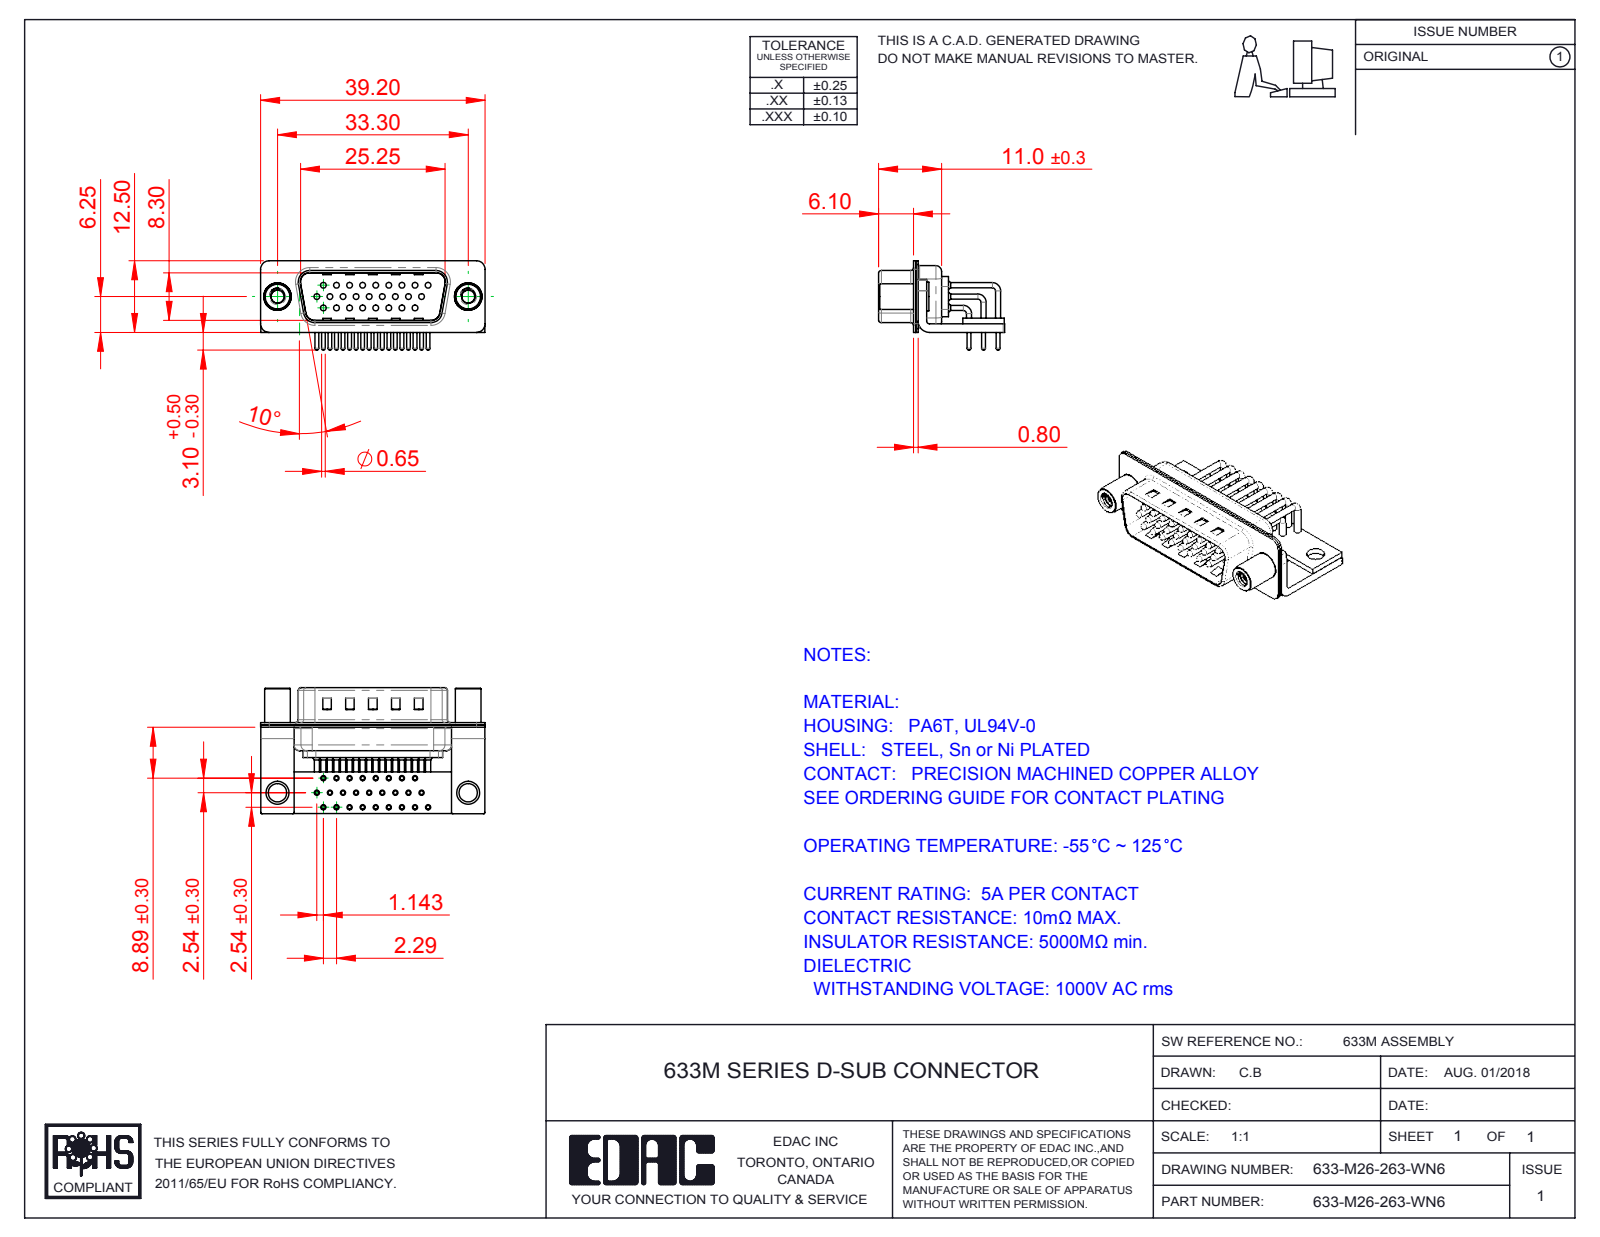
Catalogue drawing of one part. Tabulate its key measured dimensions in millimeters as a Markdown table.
| quantity | value |
| --- | --- |
| part name | 633-M26-263-WN6; 633M Stabilizer Bracket; 633M Housing_26 Contacts; 633M 4-40 Threaded Standoff (+6 more) |
| STEP written by | SolidWorks 2016 (CONFIG_CONTROL_DESIGN) |
| units | millimeters |
| bodies | 34 solids, 3352 faces (1831 planar, 1185 cylindrical, 336 other) |
| overall size | 39.2 × 22 × 15.6 |
| volume | 2 748 mm³ |
| surface area | 8 315 mm² |
| round holes (diameter × count) | 0.9 × 26, 1 × 26, 1.7 × 26, 2 × 26, 2.26 × 2, 3.2 × 2, 4 × 2, 4.8 × 2 |
| round bosses / shafts (diameter × count) | 1.5 × 26, 0.9 × 26, 0.65 × 26, 5 × 2, 4.9 × 2, 4.5 × 2 |
| partial cylindrical surfaces (radius × count) | 1.01 × 26, 0.25 × 16, 1.5 × 16, 2 × 13, 0.5 × 9, 1.6 × 8, 0.6 × 4, 0.65 × 4 |
| main face-to-face distances | 0.4, 1.5, 0.85, 0.8, 1.25, 1, 1.9, 10.4, 9.55, 2.5 |
| hole center spacings | 4.57, 2.29, 2.28, 3.96, 6.86, 4.27, 6.05, 2.78 |
